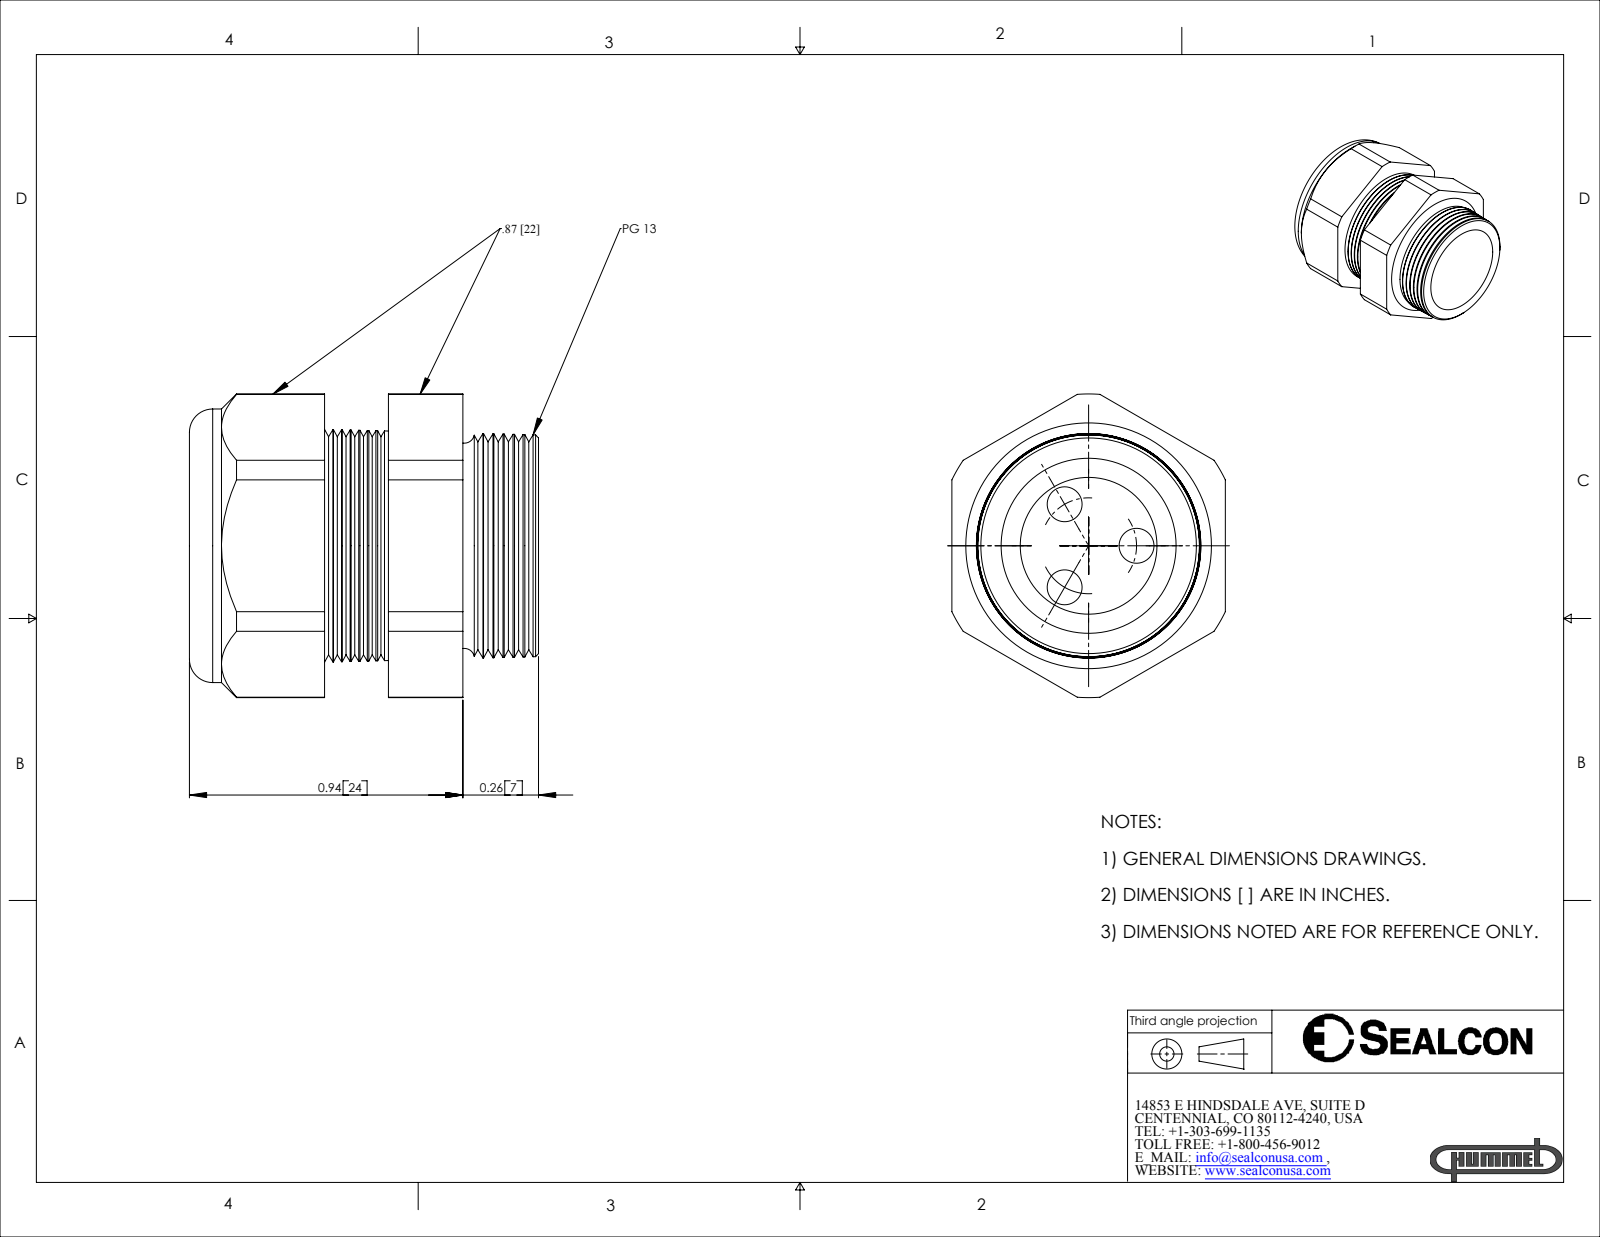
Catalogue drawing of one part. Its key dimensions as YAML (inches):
part_name: "CD13A5-BR"
step_written_by: "SolidWorks 2007 (CONFIG_CONTROL_DESIGN)"
units: inches
bodies: {solids: 2, faces: 140, planar: 20, cylindrical: 26, other: 94}
overall_size: [1.2, 1.043, 0.94]
volume: 0.532
surface_area: 8.74
round_holes:
  - {diameter: 0.12, count: 3}
  - {diameter: 0.45, count: 1}
  - {diameter: 0.47, count: 1}
round_bosses_or_shafts:
  - {diameter: 0.94, count: 1}
partial_cylinders:
  - {radius: 0.522, count: 1}
face_to_face_distances: [0.94, 0.684, 0.465, 0.22, 0.476, 0.256, 1.2, 0.735, 0.516, 0.26]
hole_center_spacings: [0.165, 0.285]
